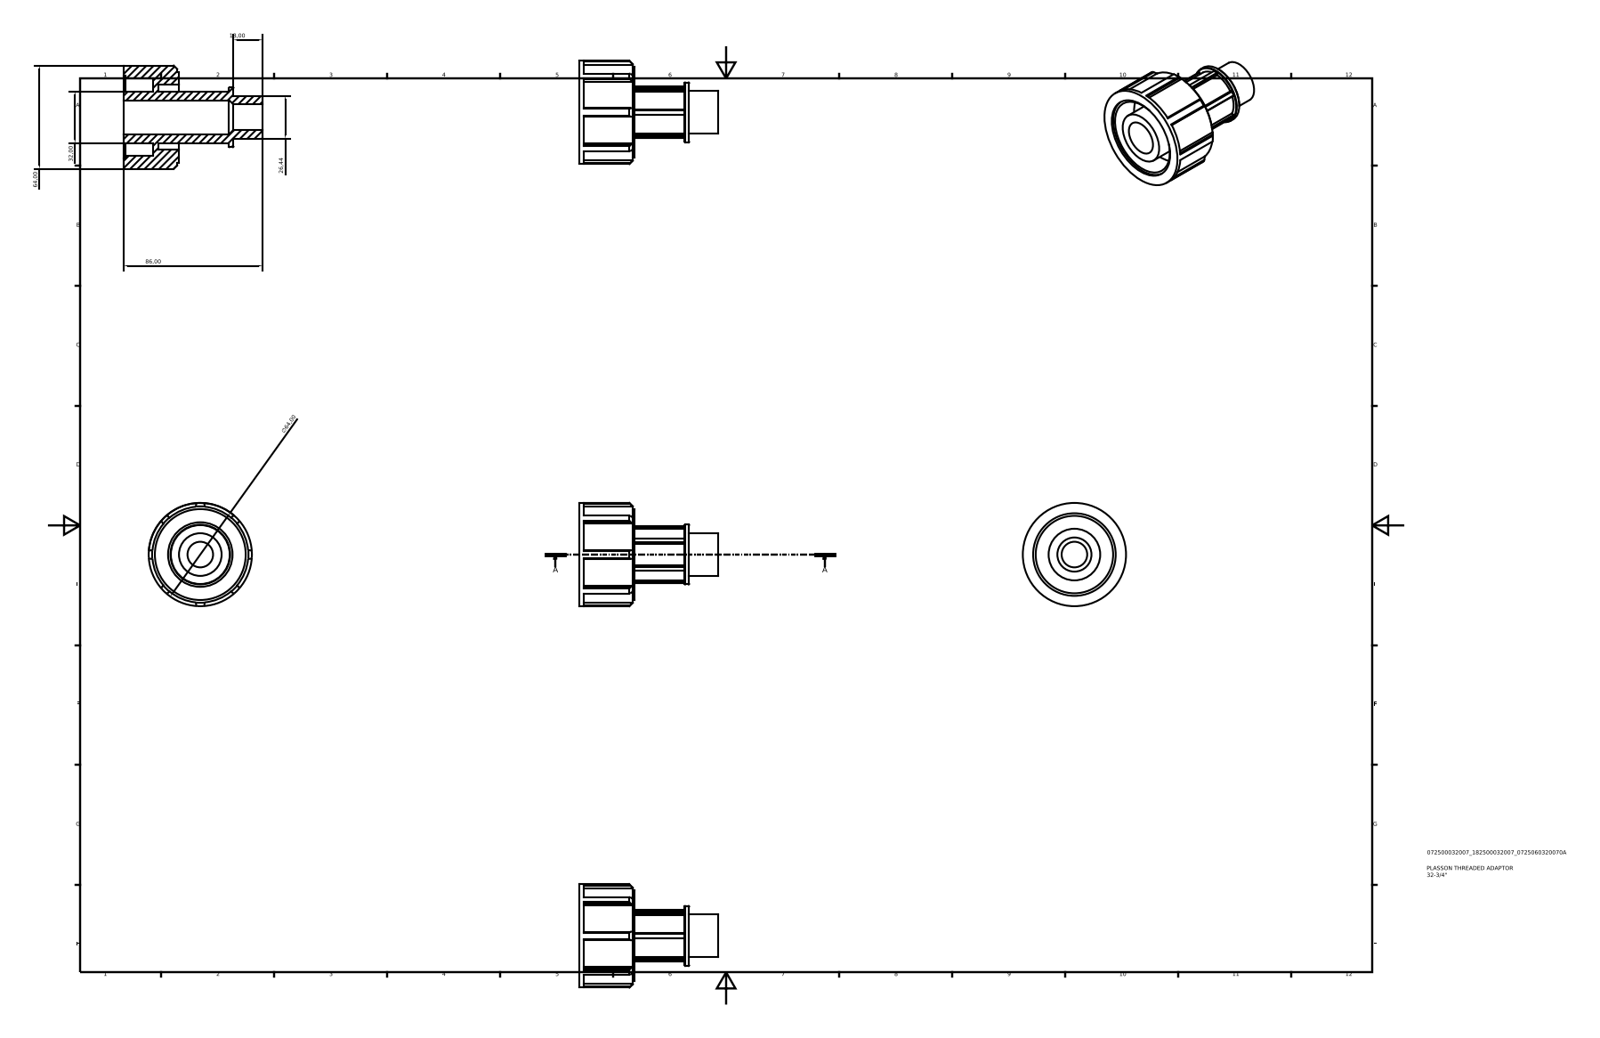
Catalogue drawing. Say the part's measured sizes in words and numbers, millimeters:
The part is named "072500032007_182500032007". Its 3-D file was written by "Autodesk Inventor 2015 (AUTOMOTIVE_DESIGN)". It is 1 solid with 115 faces: 74 planar, 30 cylindrical and 11 other. Overall it measures 86 by 64 by 64 millimeters. Its volume is 86 712 cubic millimeters and its surface area 32 242 square millimeters. Round holes: 1 of diameter 15.86, 1 of diameter 21.15, 1 of diameter 40, 1 of diameter 48, 1 of diameter 51.2. Round bosses or shafts: 1 of diameter 64, 1 of diameter 56.32, 1 of diameter 37.02, 1 of diameter 32, 1 of diameter 26.44. Partial cylindrical surfaces (rounded edges, fillets, slot ends): 1 of radius 17.6, 1 of radius 29.76. The main face-to-face distances are 18, 34.4, 16.4, 68, 1.29, 31.82, 33.11, 50, 33.6, 21.6.
